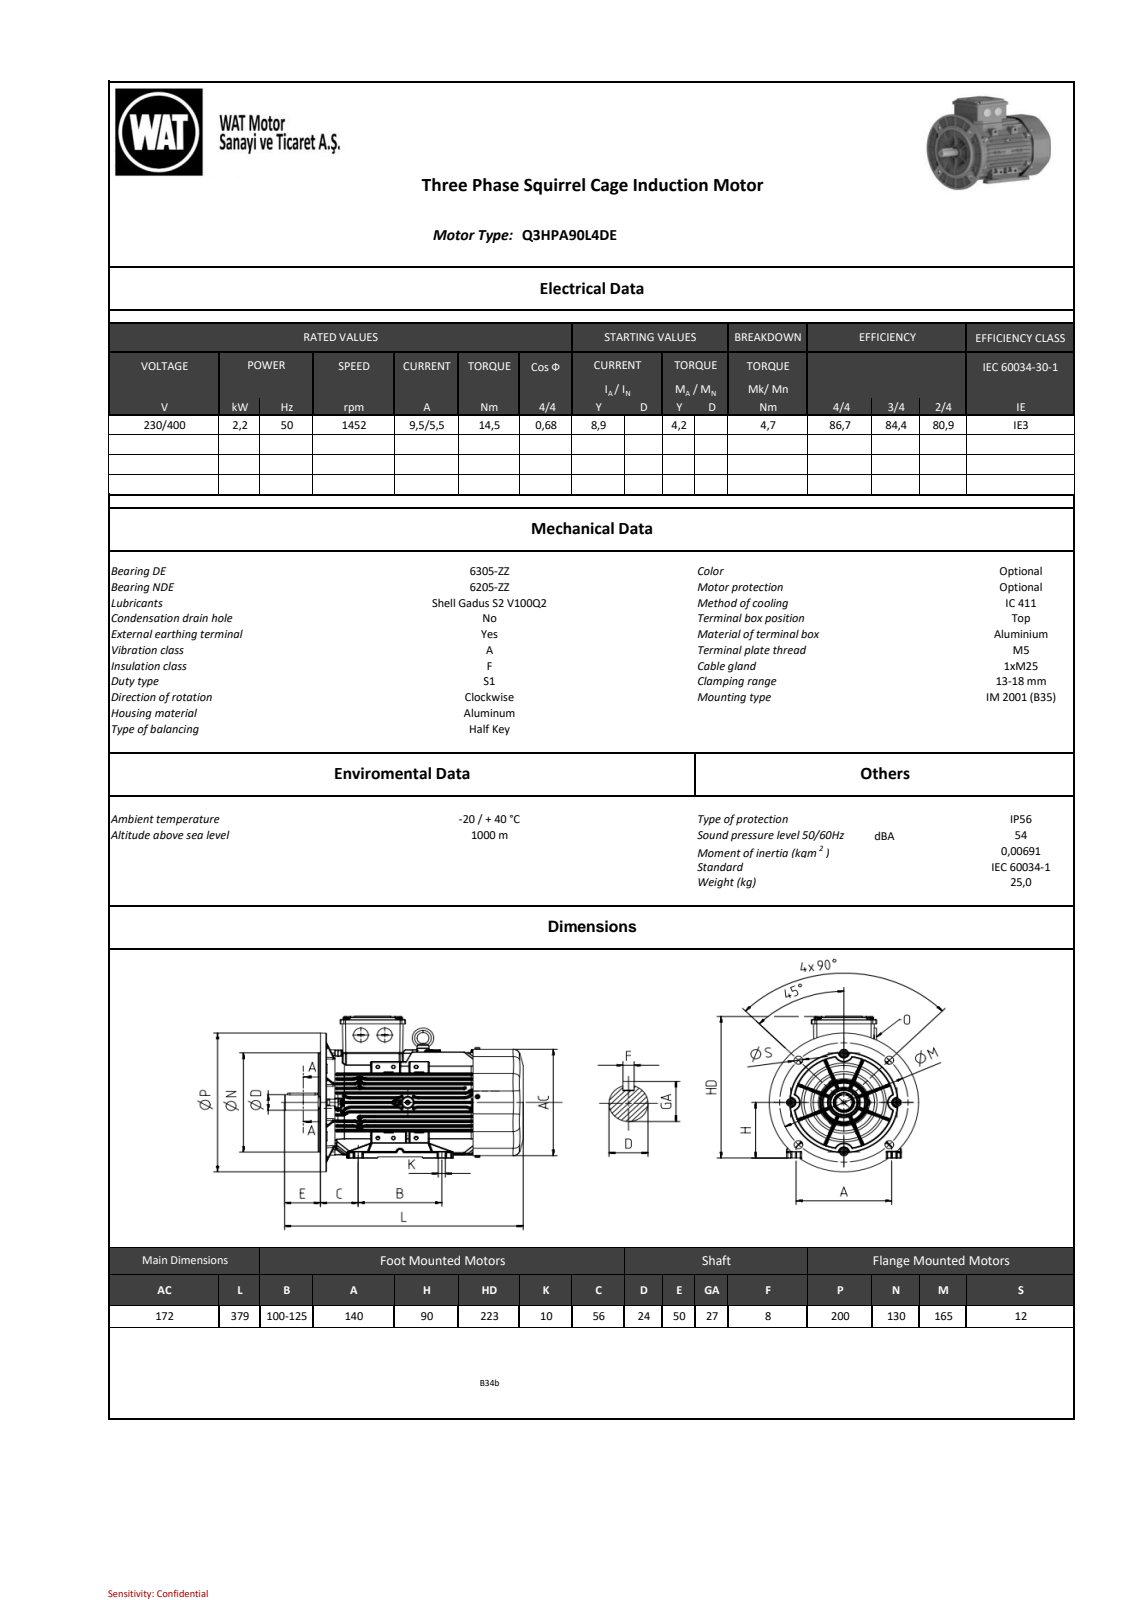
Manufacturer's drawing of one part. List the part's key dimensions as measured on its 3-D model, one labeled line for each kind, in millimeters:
Part name (STEP PRODUCT): model3_objects
STEP written by: SIEMENS PLM Software NX2206.8101 (AUTOMOTIVE_DESIGN)
Units: millimetres
Bodies: 0 solids, 7095 faces (1691 planar, 2520 cylindrical, 2884 other)
Overall size (bounding box): 378.54 × 233.05 × 200
Round holes (diameter × count): ⌀11 ×4, ⌀12 ×4, ⌀5 ×1, ⌀6.8 ×1, ⌀8.4 ×1, ⌀9.87 ×1, ⌀37.42 ×1, ⌀79.79 ×1, ⌀97.79 ×1, ⌀115.78 ×1
Round bosses / shafts (diameter × count): ⌀8 ×7, ⌀25 ×3, ⌀200 ×1, ⌀130 ×1, ⌀102.19 ×1, ⌀84.19 ×1, ⌀27.5 ×1, ⌀24 ×1
Partial cylindrical surfaces — rounded edges, fillets, slot ends (radius × count): R1 ×624, R0.8 ×574, R0.5 ×193, R0.98 ×57, R2 ×50, R8 ×28, R1.5 ×19, R4 ×10
Main face-to-face distances: 7.5, 91.91, 8.93, 82.98, 23.57, 50.35, 1.25, 7.37, 90.35, 16.87
Hole centre spacings: 62, 149.54, 79.39, 82.46, 112.27, 116.62, 82.43, 82.5
